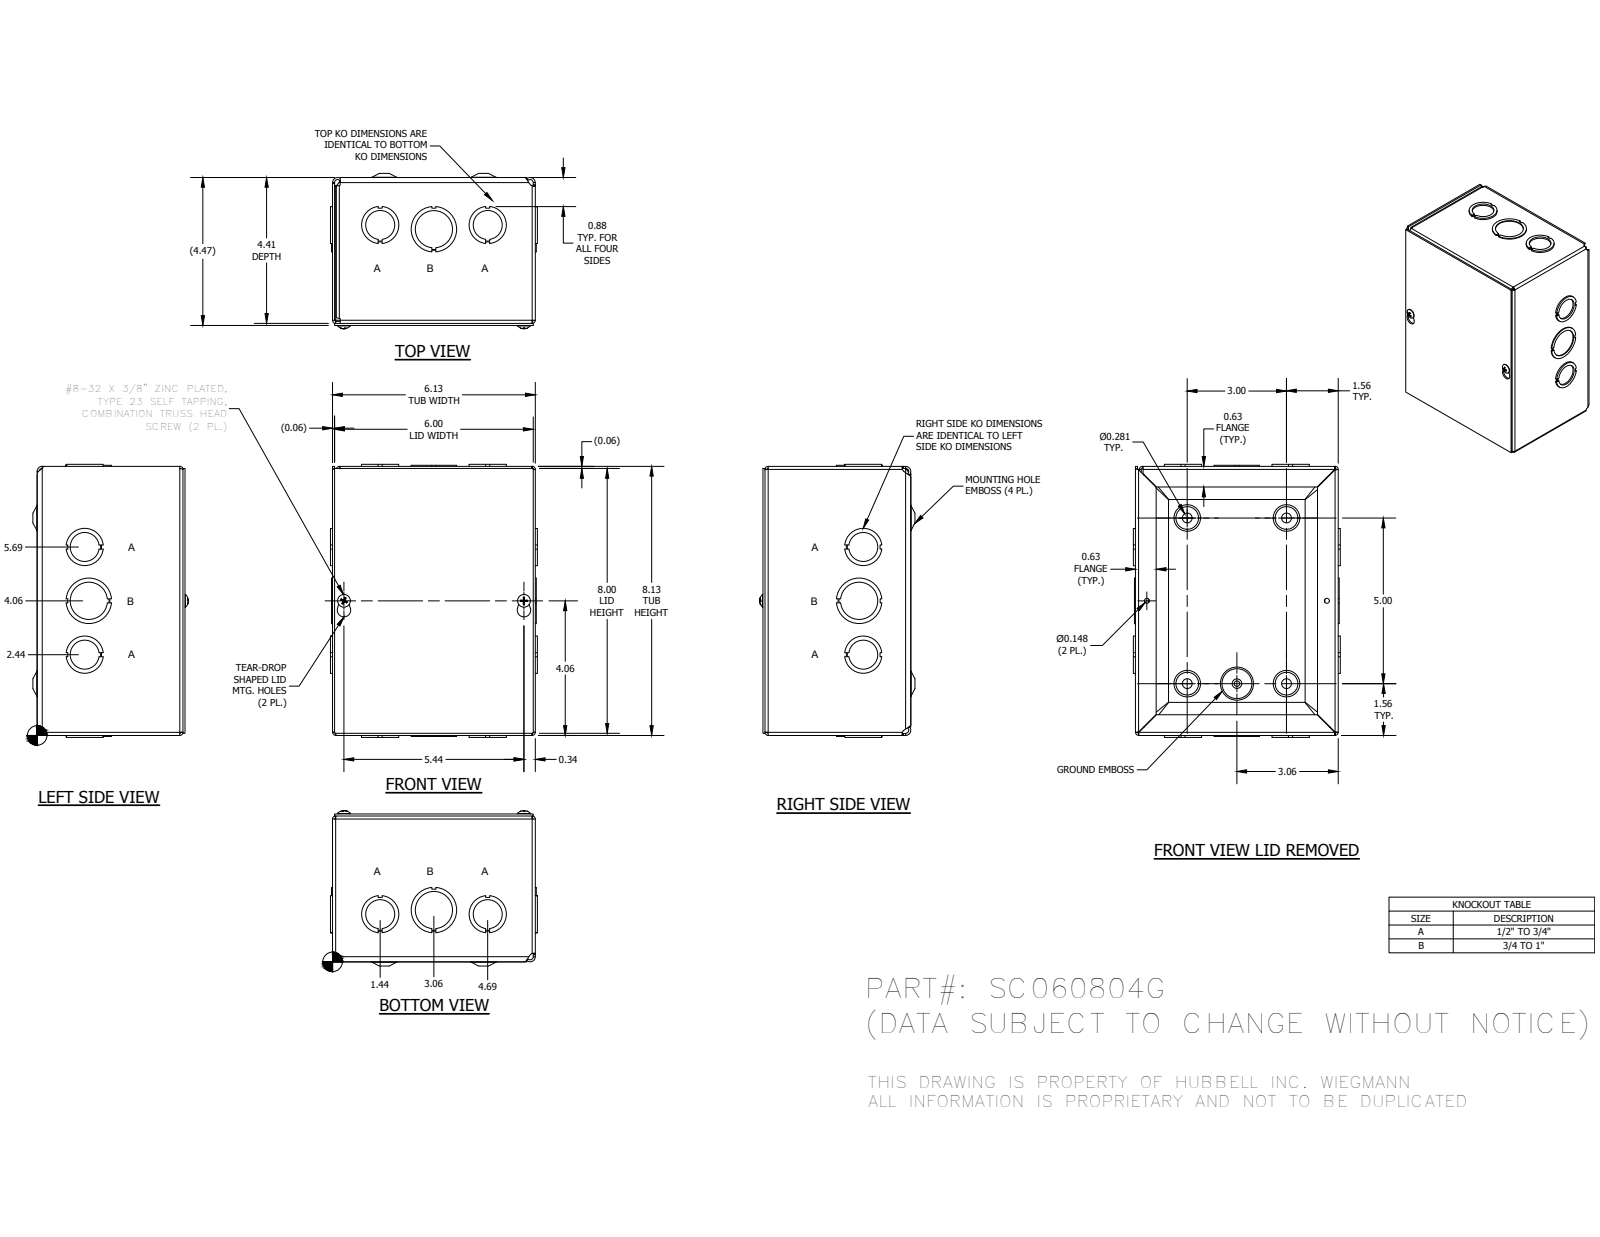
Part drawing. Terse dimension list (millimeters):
name: SC0608GBKP; SC060804GWRA; SC0608GLID; 34056 (+1 more)
written by: Autodesk Inventor 2014 (AUTOMOTIVE_DESIGN)
unit: mm
bodies: 20 solids, 630 faces (374 planar, 135 cylindrical, 121 other)
size: 209.53 × 158.72 × 119.2
holes: 6× ⌀28.57, 4× ⌀7.62, 4× ⌀22.22, 2× ⌀3.76, 2× ⌀34.92, 1× ⌀4.19
bosses: 2× ⌀9.75, 2× ⌀4.17, 1× ⌀5.8
rounds: 8× R0.79, 8× R2.37, 4× R1.4, 4× R1.57, 4× R2.38, 4× R2.79, 4× R2.97, 4× R3.15
face distances: 1.57, 110.32, 154, 111.89, 1.58, 1.59, 111.91, 113.48, 155.57, 152.43
hole spacings: 38.1, 41.39, 41.4, 70.64, 70.65, 76.2, 82.55, 124.55
